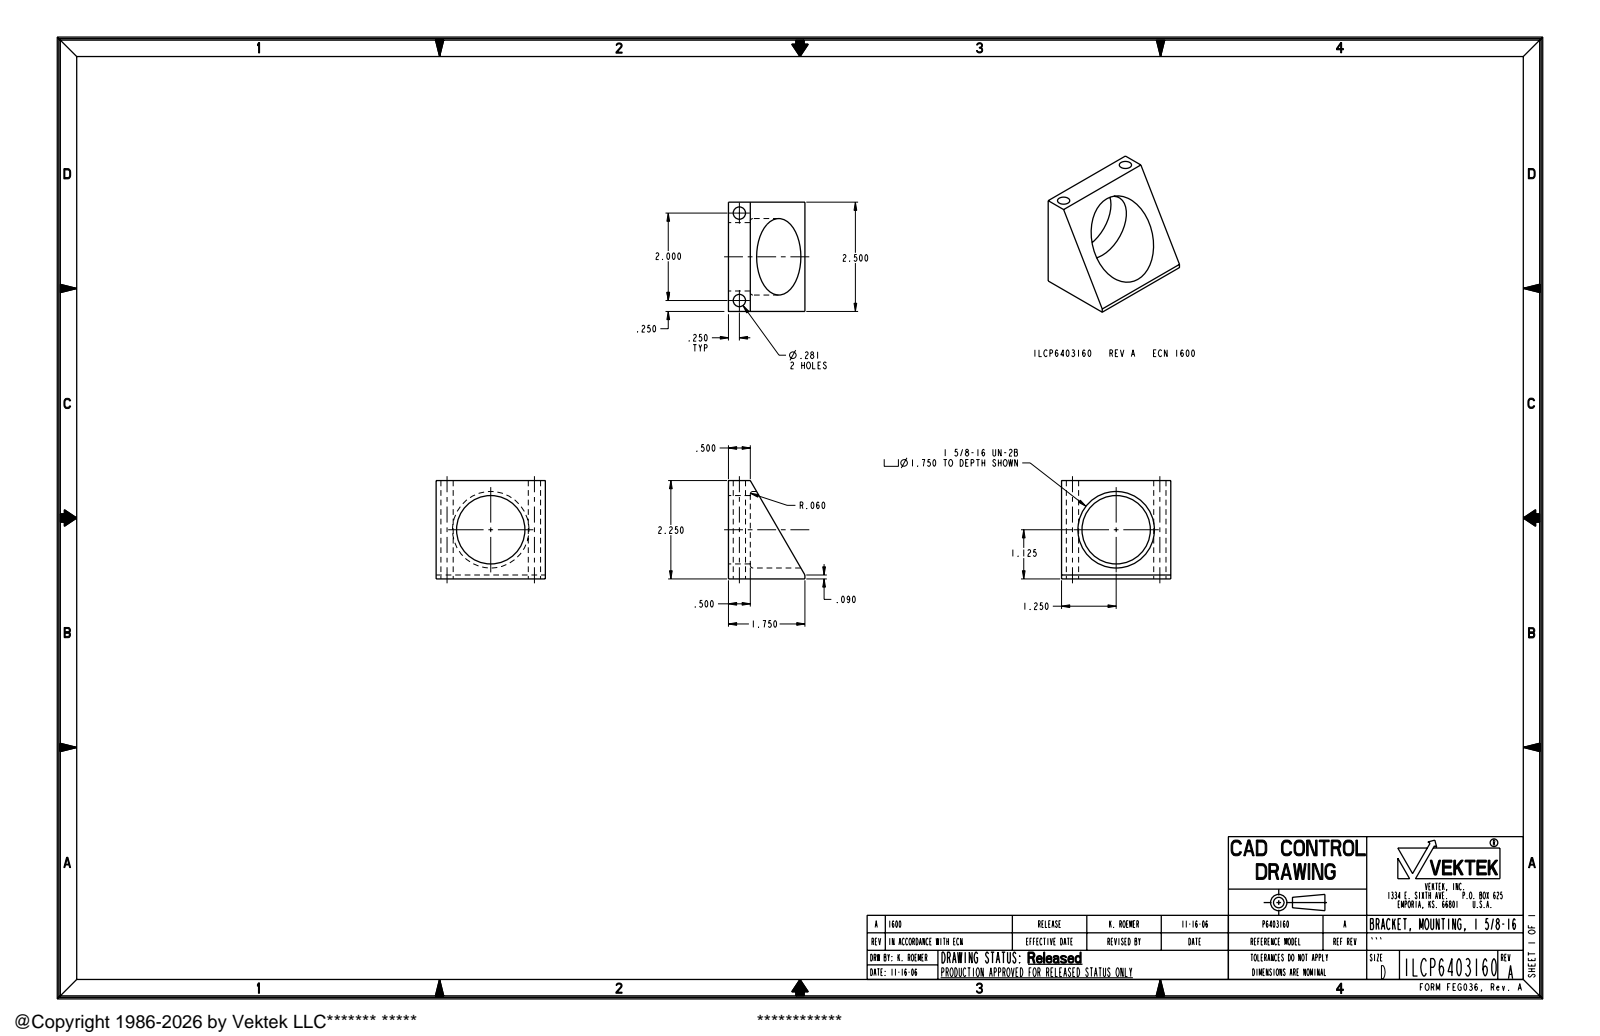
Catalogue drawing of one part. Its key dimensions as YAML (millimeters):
part_name: "ILCP6403160"
step_written_by: "PRO/ENGINEER BY PARAMETRIC TECHNOLOGY CORPORATION, 2005180 (AUTOMOTIVE_DESIGN_CC2)"
units: millimeters
bodies: {solids: 1, faces: 18, planar: 8, cylindrical: 8, other: 2}
overall_size: [63.5, 57.2, 44.5]
volume: 60090
surface_area: 18250
round_holes:
  - {diameter: 7.1, count: 2}
  - {diameter: 39.7, count: 1}
  - {diameter: 44.5, count: 1}
face_to_face_distances: [63.5, 57.2, 44.5, 31.8, 12.7]
hole_center_spacings: [50.8]
